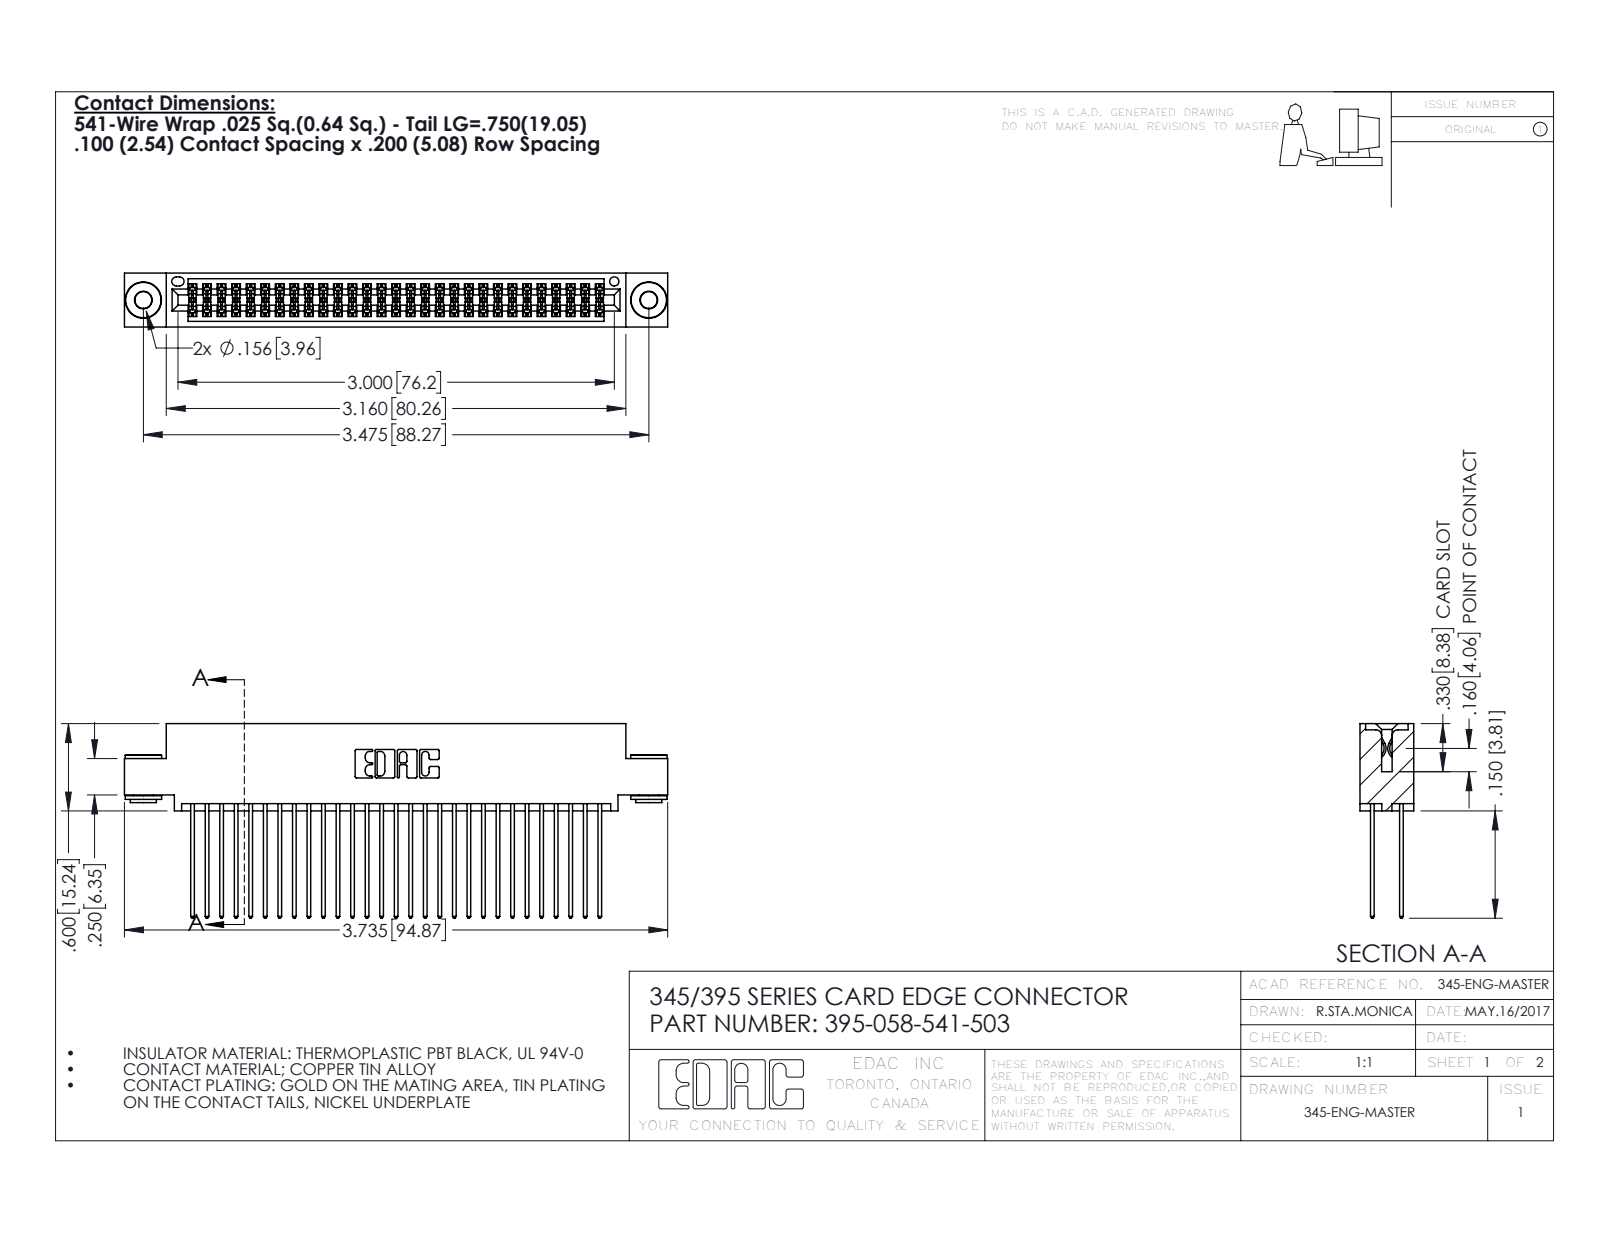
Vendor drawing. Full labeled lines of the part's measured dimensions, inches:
Part name (STEP PRODUCT): 345 Part_0.110 Offset - 0.156 Dia-TH; 345-292-001_345-293-141; 345-250-002_345-250-002-102; 395-058-541-503
STEP written by: SolidWorks 2016 (CONFIG_CONTROL_DESIGN)
Units: inches
Bodies: 61 solids, 3068 faces (2008 planar, 1052 cylindrical, 8 other)
Overall size (bounding box): 3.735 × 1.337 × 0.37
Volume: 0.572 in³ · Surface area: 23.97 in²
Round holes (diameter × count): ⌀0.116 ×2, ⌀0.156 ×2, ⌀0.064 ×1
Round bosses / shafts (diameter × count): ⌀0.25 ×2, ⌀0.18 ×2, ⌀0.136 ×2
Partial cylindrical surfaces — rounded edges, fillets, slot ends (radius × count): R0.006 ×87, R0.01 ×58, R0.01 ×22, R0.007 ×6, R0.031 ×6, R0.026 ×3, R0.014 ×2, R0.019 ×2
Main face-to-face distances: 0.072, 0.298, 0.2, 0.025, 0.098, 0.272, 0.225, 0.37, 0.175, 0.149
Hole centre spacings: 0.27, 3.24, 3.475
